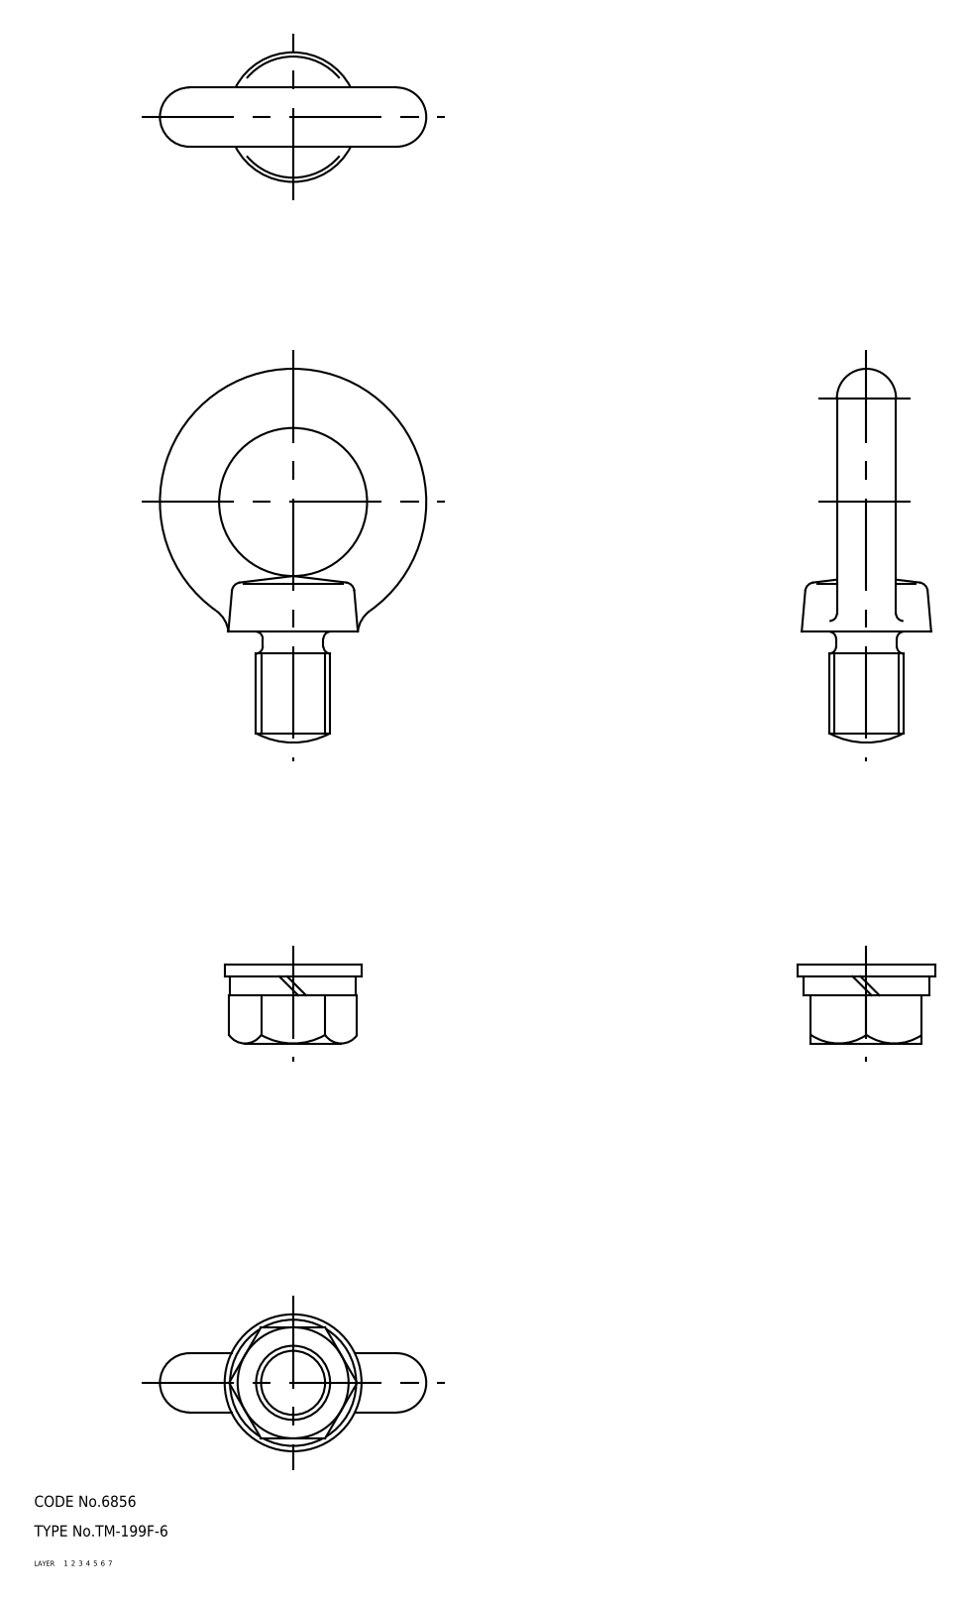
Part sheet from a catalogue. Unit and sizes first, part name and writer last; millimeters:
Units: millimetres
Overall size (bounding box): 101 × 72 × 37
Round holes (diameter × count): ⌀20 ×1
Round bosses / shafts (diameter × count): ⌀37 ×1, ⌀34.1 ×1
Main face-to-face distances: 3.2, 5.1, 8.3, 30, 13, 18.1, 21.3
Volume: 62 533 mm³ · Surface area: 19 091 mm²
Bodies: 4 solids, 56 faces (13 planar, 12 cylindrical, 31 other)
Part name (STEP PRODUCT): TM_199F_6
STEP written by: SolidWorks 2003240 (AUTOMOTIVE_DESIGN)
